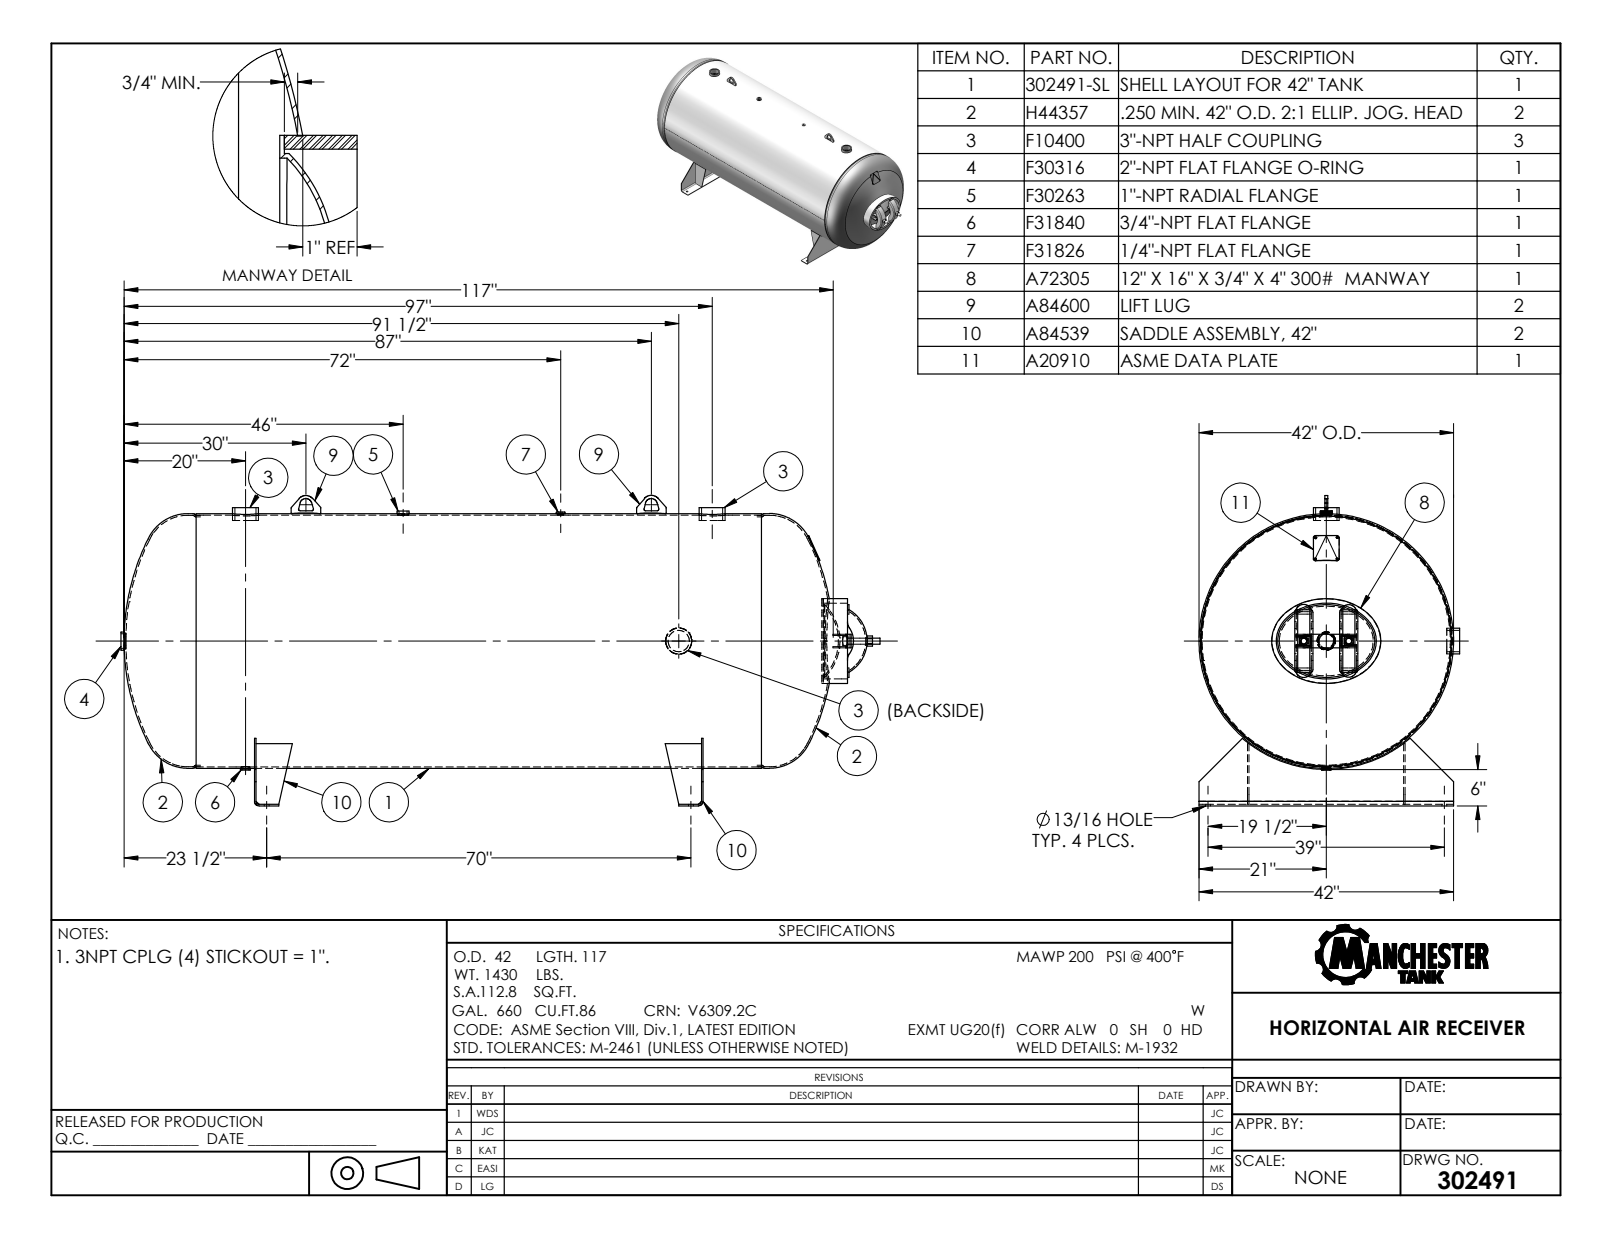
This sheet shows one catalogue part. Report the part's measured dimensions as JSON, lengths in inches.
{"part_name": "302491", "step_written_by": "SolidWorks 2011 (CONFIG_CONTROL_DESIGN)", "units": "inches", "bodies": {"solids": 0, "faces": 252, "planar": 111, "cylindrical": 79, "other": 62}, "overall_size": [123.371, 51, 43], "round_holes": [[0.813, 4], [3.5, 3], [1.125, 2], [0.54, 1], [1.05, 1], [1.315, 1], [2.375, 1], [41.5, 1]], "round_bosses_or_shafts": [[4.25, 3], [1, 2], [42, 1], [41.437, 1], [3.5, 1], [2.875, 1], [2.375, 1], [2.063, 1]], "partial_cylinders_radius": [[1.318, 4], [0.375, 3], [0.063, 2], [0.313, 2], [3, 2], [5.917, 1], [6, 1], [27.06, 1]], "face_to_face_distances": [0.25, 73.75, 74, 73.5, 25.75, 26, 25.5, 9.625, 9.875, 83.375], "hole_center_spacings": [20.261, 29.026, 52.273, 77.978, 27, 39, 54, 70]}
